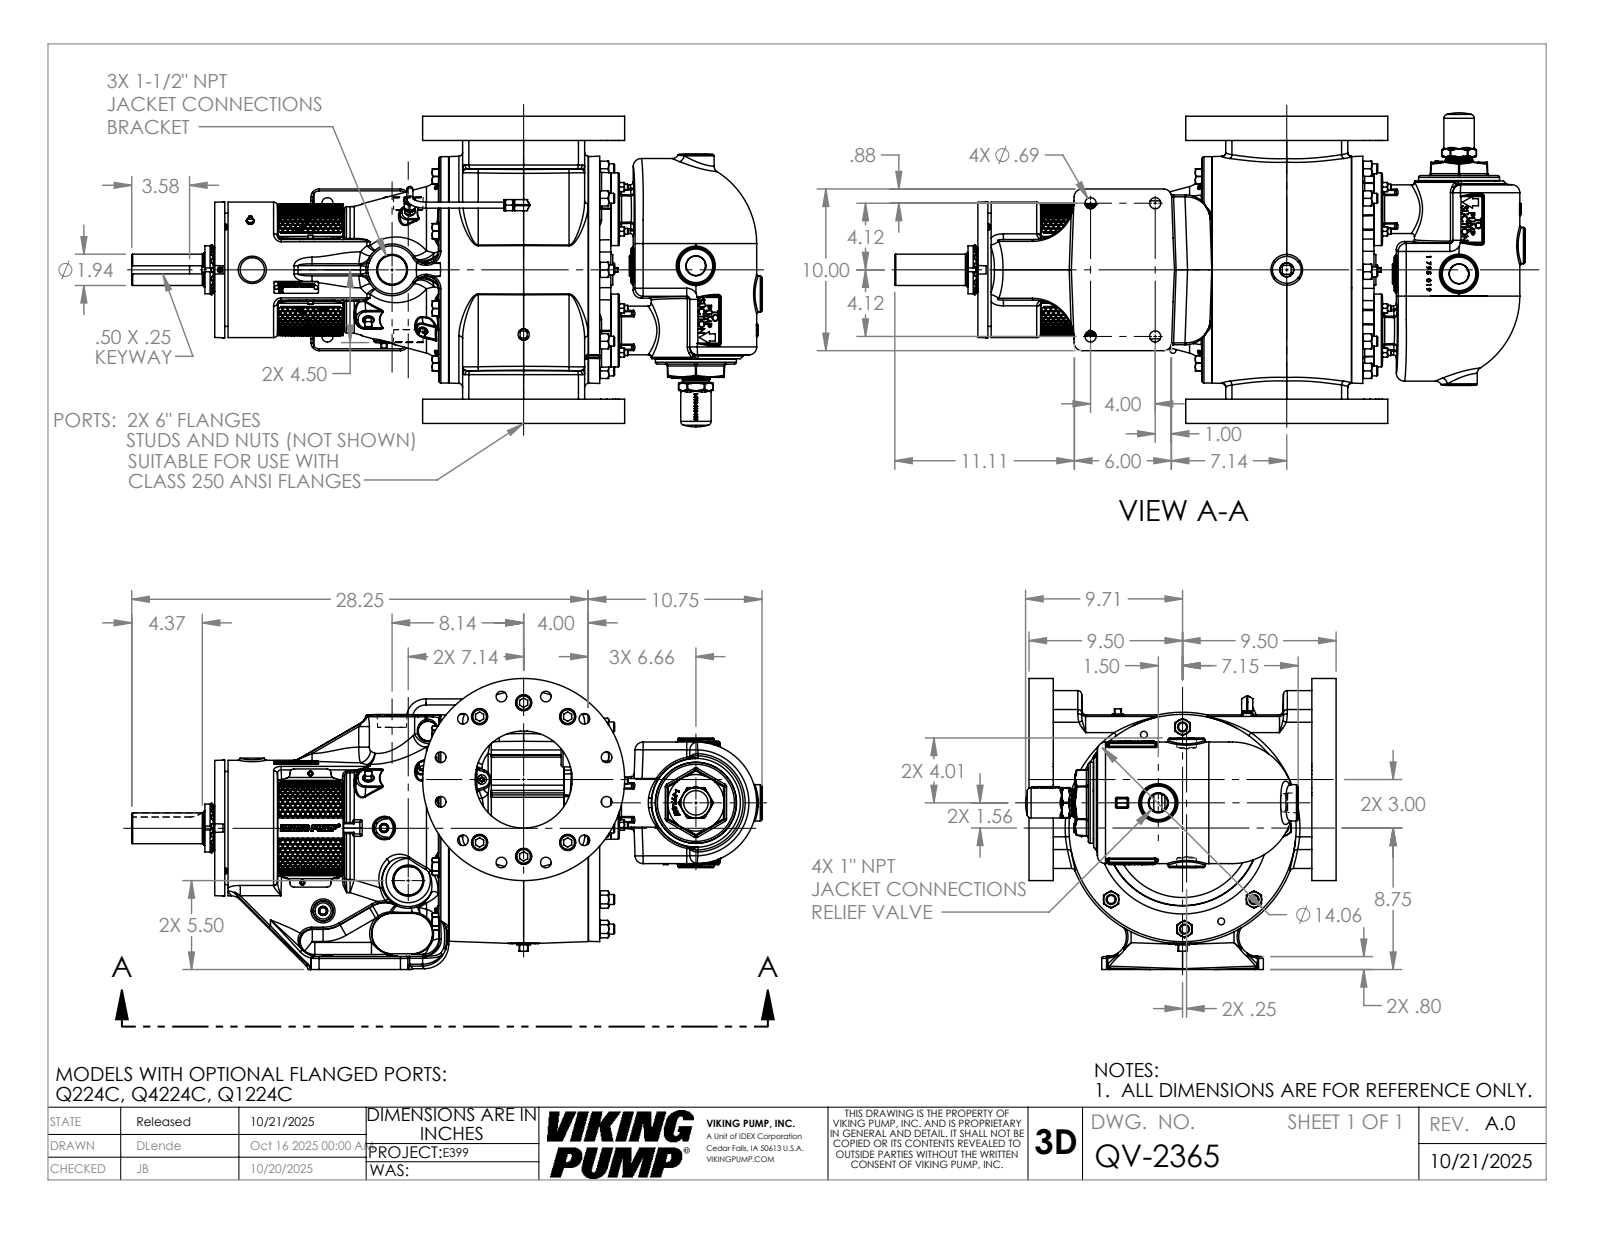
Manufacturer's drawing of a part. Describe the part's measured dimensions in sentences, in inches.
The part is named "QV-2365". Its 3-D file was written by "SolidWorks 2024 (AUTOMOTIVE_DESIGN)". It is 1 solid with 5174 faces: 1661 planar, 772 cylindrical and 2741 other. Overall it measures 38.999 by 19.214 by 18 inches. Its volume is 3 504 cubic inches and its surface area 2 996 square inches. Round holes: 12 of diameter 0.656, 9 of diameter 0.25, 8 of diameter 0.266, 8 of diameter 1.157, 7 of diameter 1, 4 of diameter 0.688, 2 of diameter 0.159, 2 of diameter 0.313, 2 of diameter 0.422, 1 of diameter 0.453, 1 of diameter 1.435, 1 of diameter 2.157. Round bosses or shafts: 8 of diameter 0.617, 8 of diameter 0.369, 6 of diameter 0.937, 5 of diameter 0.375, 3 of diameter 0.312, 3 of diameter 0.19, 2 of diameter 4.5, 2 of diameter 0.687. Partial cylindrical surfaces (rounded edges, fillets, slot ends): 60 of radius 0.12, 28 of radius 0.5, 26 of radius 0.06, 22 of radius 0.75, 18 of radius 0.015, 18 of radius 0.092, 16 of radius 0.07, 16 of radius 0.19. The main face-to-face distances are 1.5, 17.5, 19, 16, 0.57, 23.817, 3.82, 19.998, 22.268, 7.972. The hole center spacings are 5.313, 3.75, 2.079, 10.263, 5.783, 2.713, 2.75, 3.133.
